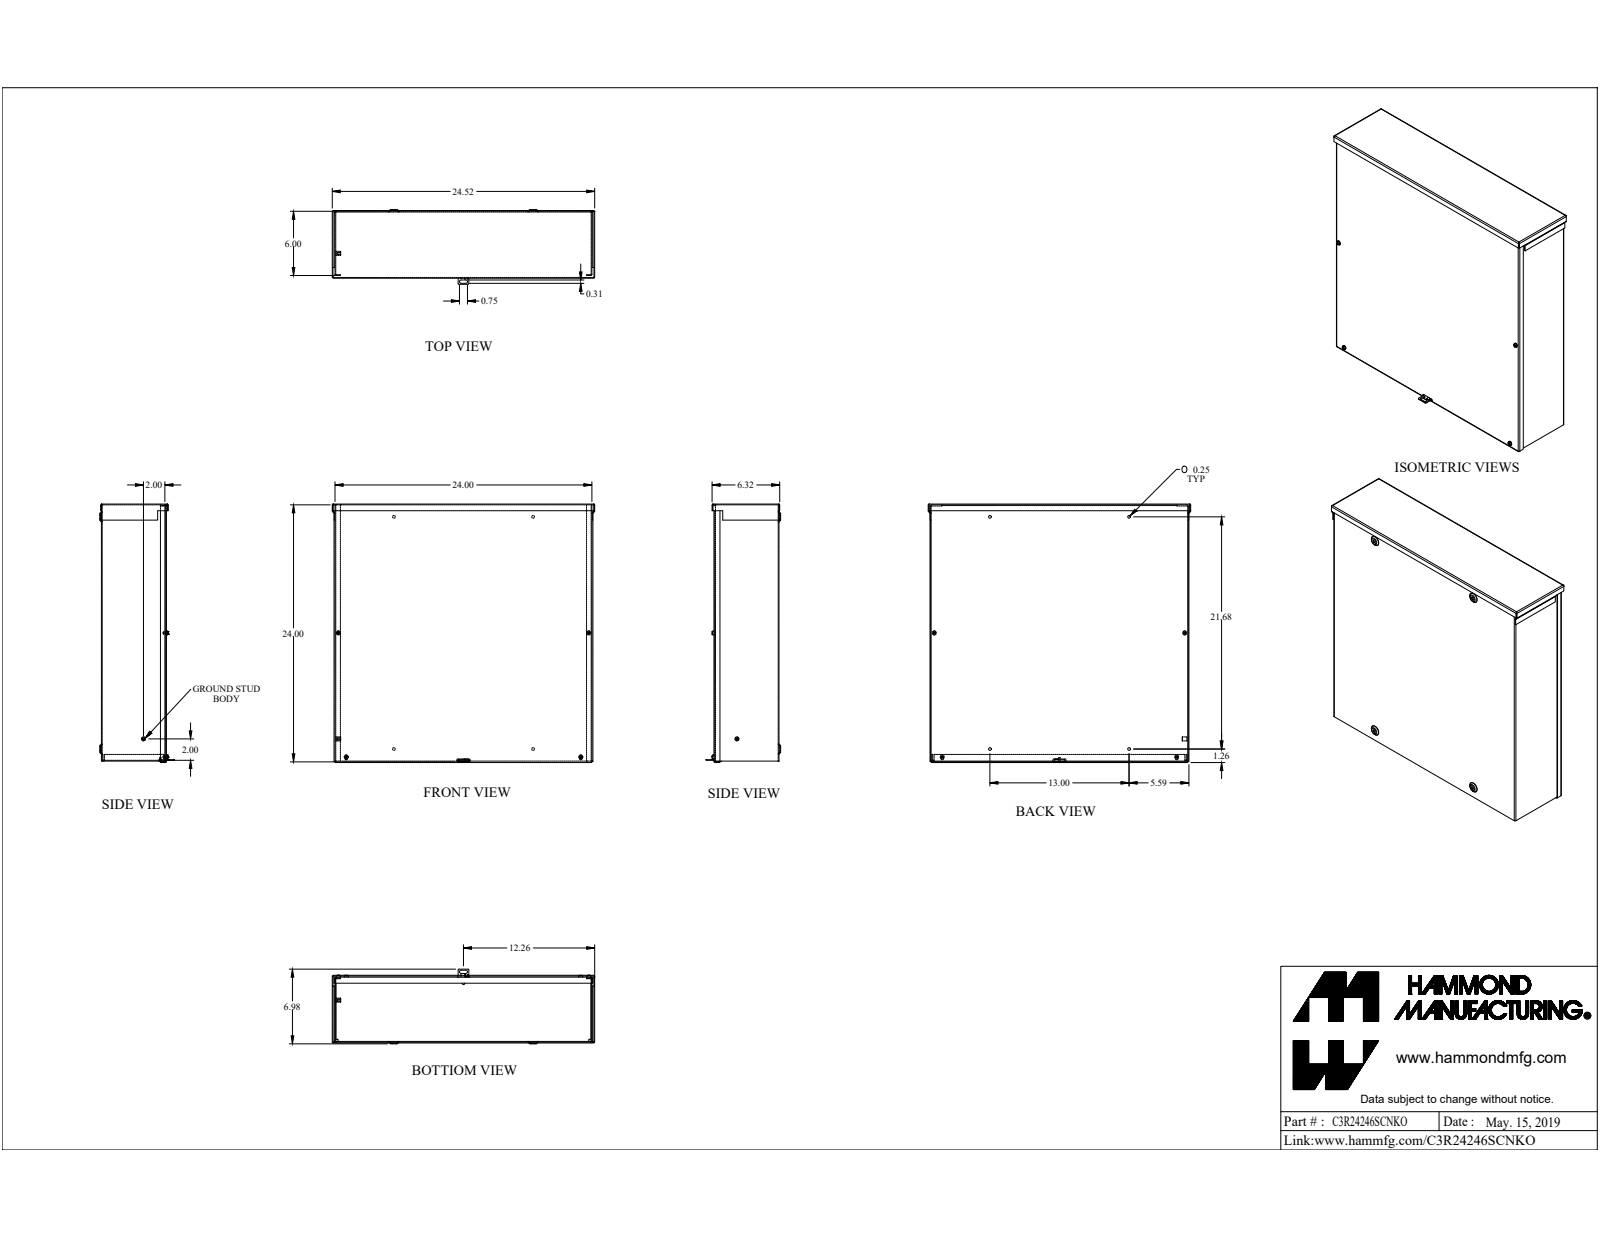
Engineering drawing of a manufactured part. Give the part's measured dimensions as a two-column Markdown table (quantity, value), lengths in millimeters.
| quantity | value |
| --- | --- |
| part name | C3R24246SCNKO |
| STEP written by | SolidWorks 2019 (AUTOMOTIVE_DESIGN) |
| units | millimeters |
| bodies | 11 solids, 339 faces (211 planar, 84 cylindrical, 44 other) |
| overall size | 622.8 × 613 × 177.2 |
| volume | 2 181 000 mm³ |
| surface area | 2 426 000 mm² |
| round holes (diameter × count) | 4.3 × 4, 6.4 × 4, 3.2 × 1, 3.5 × 1, 4 × 1 |
| round bosses / shafts (diameter × count) | 4.8 × 4, 9.5 × 3, 9.5 × 2, 3.2 × 1 |
| partial cylindrical surfaces (radius × count) | 0.9 × 20, 2.7 × 20, 2.8 × 8, 3.2 × 8, 4 × 2, 0.7 × 1, 2.2 × 1 |
| main face-to-face distances | 1.8, 152.4, 150.6, 154.2, 607.8, 609.6, 1.8, 605.9, 605.9, 607.8 |
| hole center spacings | 305.3, 538, 115, 296.7, 330.2, 443.8, 550.6, 582.5 |
